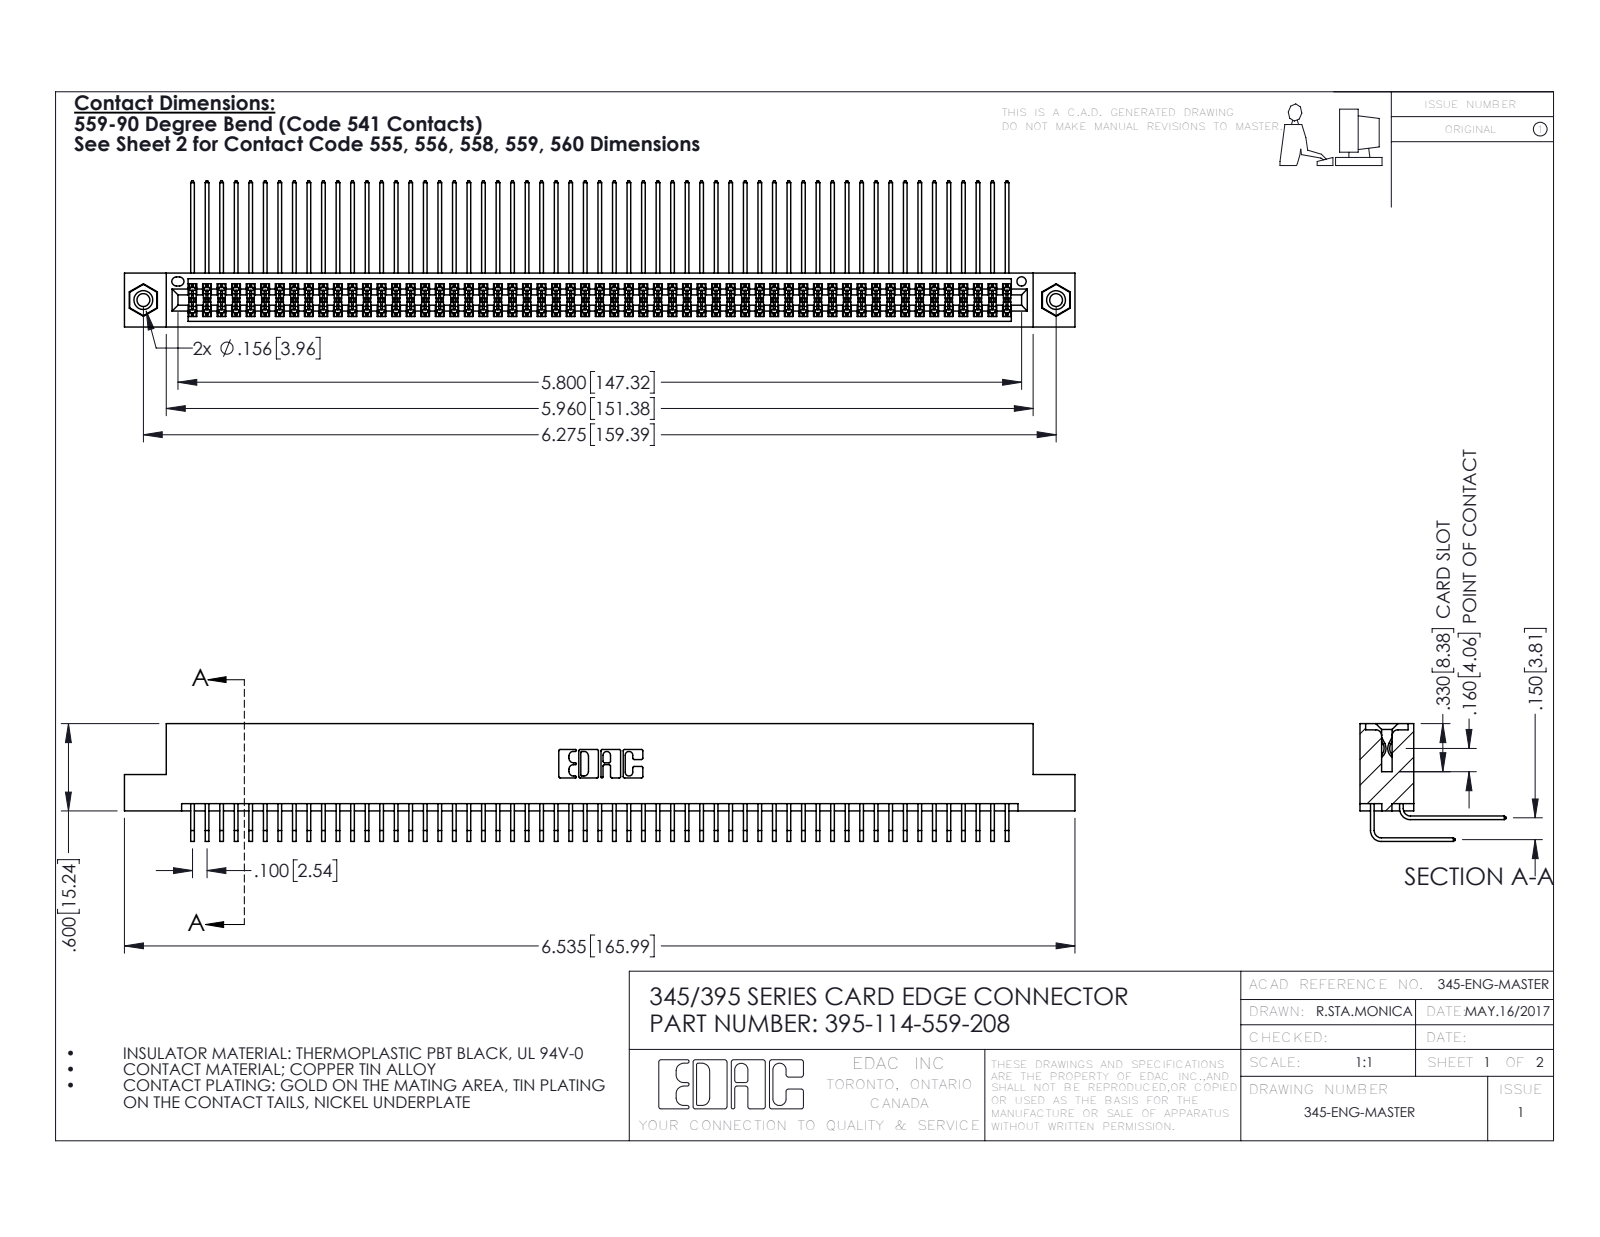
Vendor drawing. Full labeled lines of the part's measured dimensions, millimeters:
Part name (STEP PRODUCT): 395-114-559-208; 345-292-001_559 Tail - 2; 345-292-001_558 559 Tail - 1; 345-250-001_345-250-003-102 (+1 more)
STEP written by: SolidWorks 2016 (CONFIG_CONTROL_DESIGN)
Units: millimetres
Bodies: 117 solids, 6114 faces (4102 planar, 1996 cylindrical, 16 other)
Overall size (bounding box): 166 × 25.5 × 20.5
Volume: 16 910 mm³ · Surface area: 28 400 mm²
Round holes (diameter × count): ⌀2.3 ×2, ⌀3.2 ×2, ⌀4 ×2, ⌀1.6 ×1
Round bosses / shafts (diameter × count): ⌀3.9 ×2
Partial cylindrical surfaces — rounded edges, fillets, slot ends (radius × count): R0.2 ×172, R0.3 ×22, R0.2 ×6, R0.8 ×6, R0.7 ×3, R0.4 ×2, R0.5 ×2, R0.6 ×2
Main face-to-face distances: 1.8, 7.6, 5.1, 9.4, 2.5, 6.9, 0.6, 5.7, 4.4, 3.8
Hole centre spacings: 6.9, 153.4, 159.4
